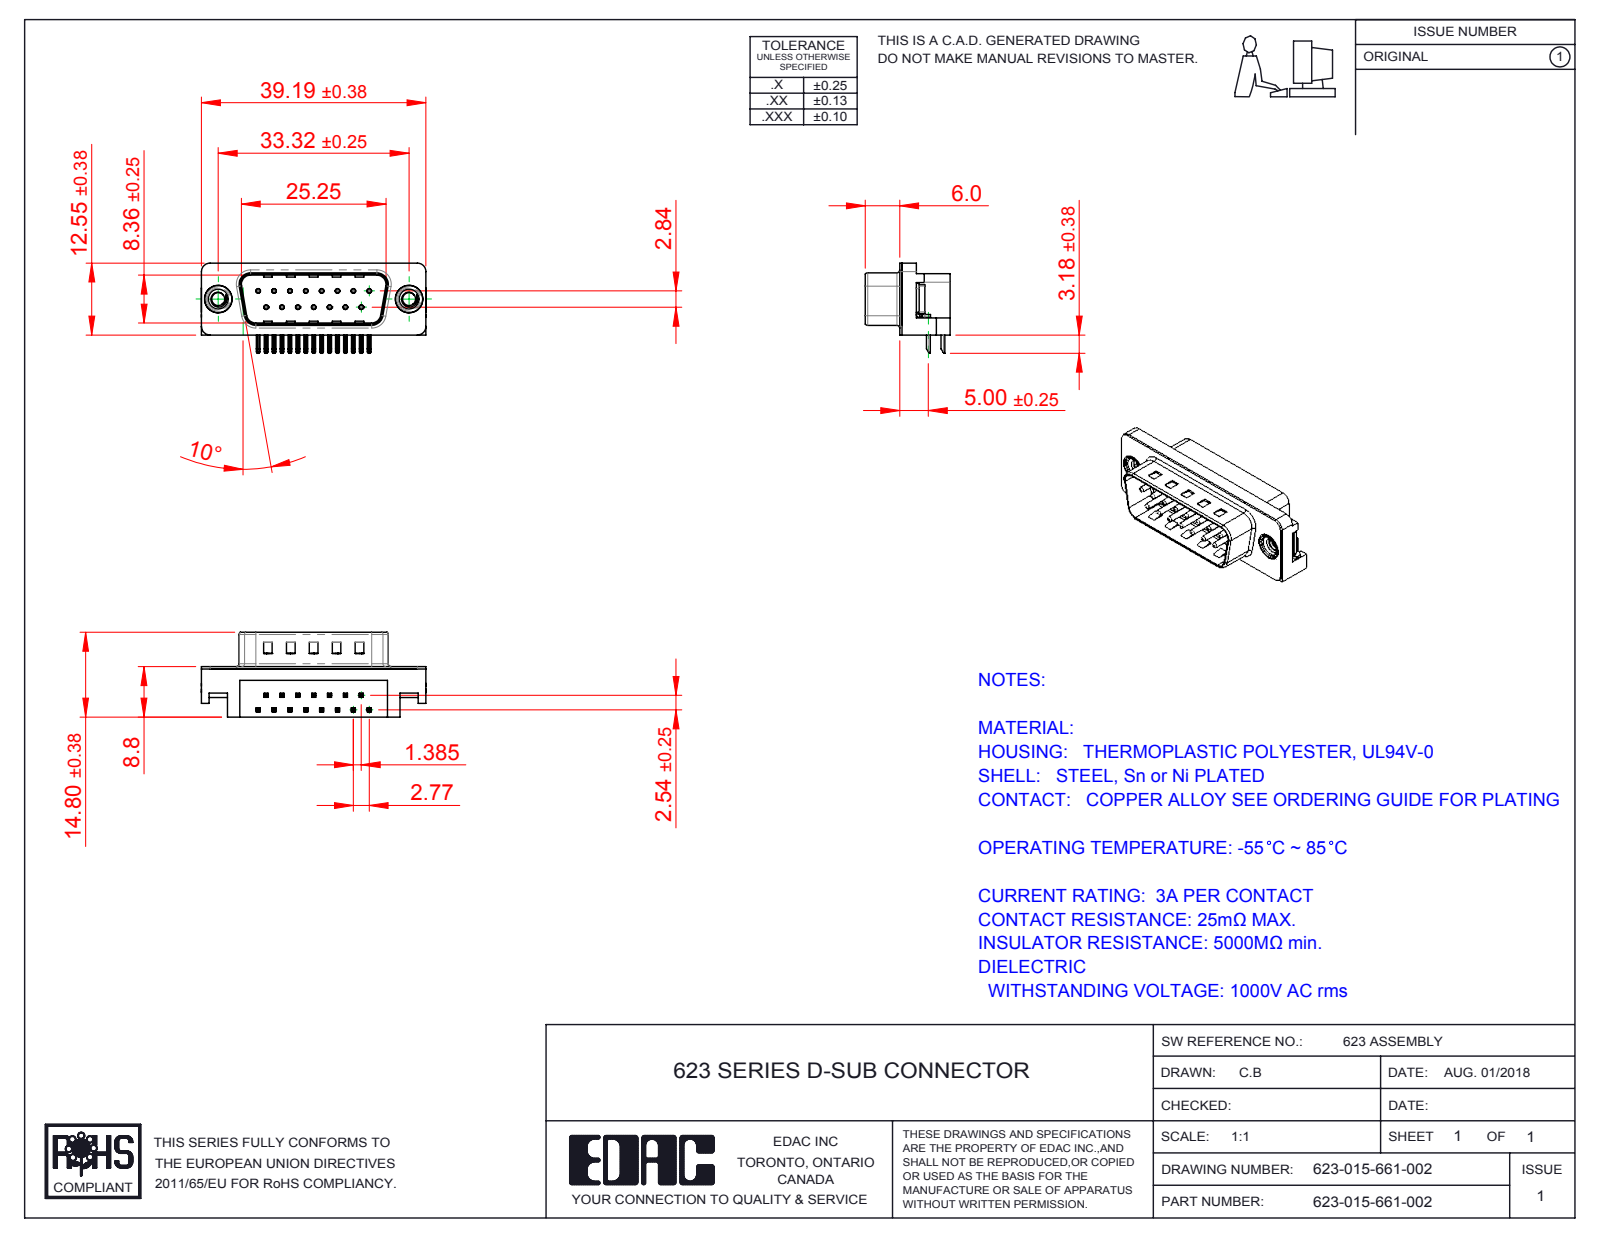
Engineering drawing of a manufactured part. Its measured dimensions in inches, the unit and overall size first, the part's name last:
Units: inches
Overall size (bounding box): 1.544 × 0.619 × 0.583
Round holes (diameter × count): ⌀0.014 ×15, ⌀0.031 ×15, ⌀0.089 ×2, ⌀0.157 ×2, ⌀0.189 ×2, ⌀0.197 ×2
Round bosses / shafts (diameter × count): ⌀0.03 ×15, ⌀0.193 ×2, ⌀0.187 ×2, ⌀0.154 ×2
Partial cylindrical surfaces — rounded edges, fillets, slot ends (radius × count): R0.01 ×68, R0.005 ×30, R0.039 ×16, R0.02 ×9, R0.059 ×6, R0.035 ×4, R0.063 ×4, R0.079 ×4
Main face-to-face distances: 0.016, 0.331, 0.083, 0.067, 0.412, 0.346, 0.428, 0.345, 0.232, 0.114
Hole centre spacings: 0.124, 0.109, 0.218, 0.327, 0.436, 0.198, 0.198, 0.294
Volume: 0.203 in³ · Surface area: 7.572 in²
Bodies: 21 solids, 1467 faces (893 planar, 435 cylindrical, 139 other)
Part name (STEP PRODUCT): 623 Non Board Mount; 623 Shell_15 Socket; 623 4-40 Threaded Rivet; 623 Contact Top (+3 more)
STEP written by: SolidWorks 2016 (CONFIG_CONTROL_DESIGN)
